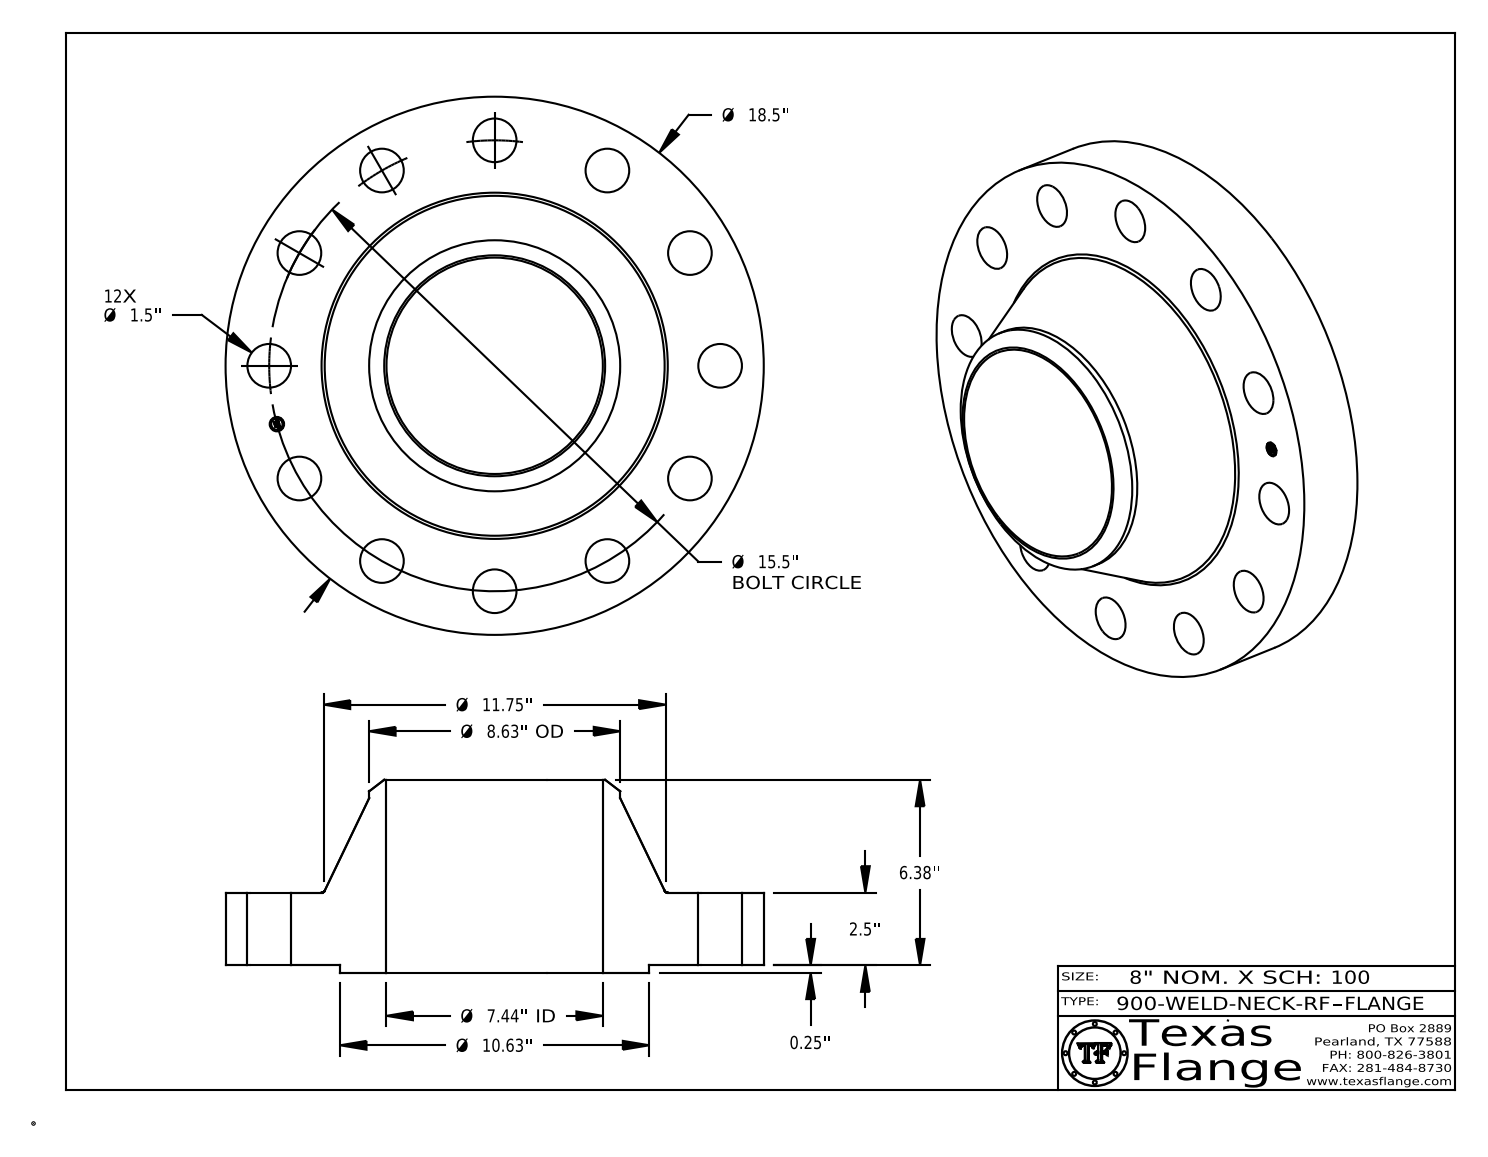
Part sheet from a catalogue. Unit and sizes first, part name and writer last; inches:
Units: inches
Overall size (bounding box): 18.5 × 18.5 × 6.63
Round holes (diameter × count): ⌀1.5 ×12, ⌀0.495 ×1, ⌀7.437 ×1
Round bosses / shafts (diameter × count): ⌀0.03 ×8, ⌀18.5 ×1, ⌀10.63 ×1, ⌀8.63 ×1, ⌀0.39 ×1
Main face-to-face distances: 2.5, 0.25, 2.75, 6.63, 6.38, 3.88, 0.015, 2.735, 2.485, 3.895
Hole centre spacings: 7.75, 7.75, 13.424, 4.012, 10.961, 14.972, 4.011, 10.96
Volume: 654.4 in³ · Surface area: 932.9 in²
Bodies: 1 solid, 427 faces (369 planar, 52 cylindrical, 6 other)
Part name (STEP PRODUCT): 900-WELD-NECK-RF
STEP written by: CATIA V5 STEP AP214 (AUTOMOTIVE_DESIGN)
